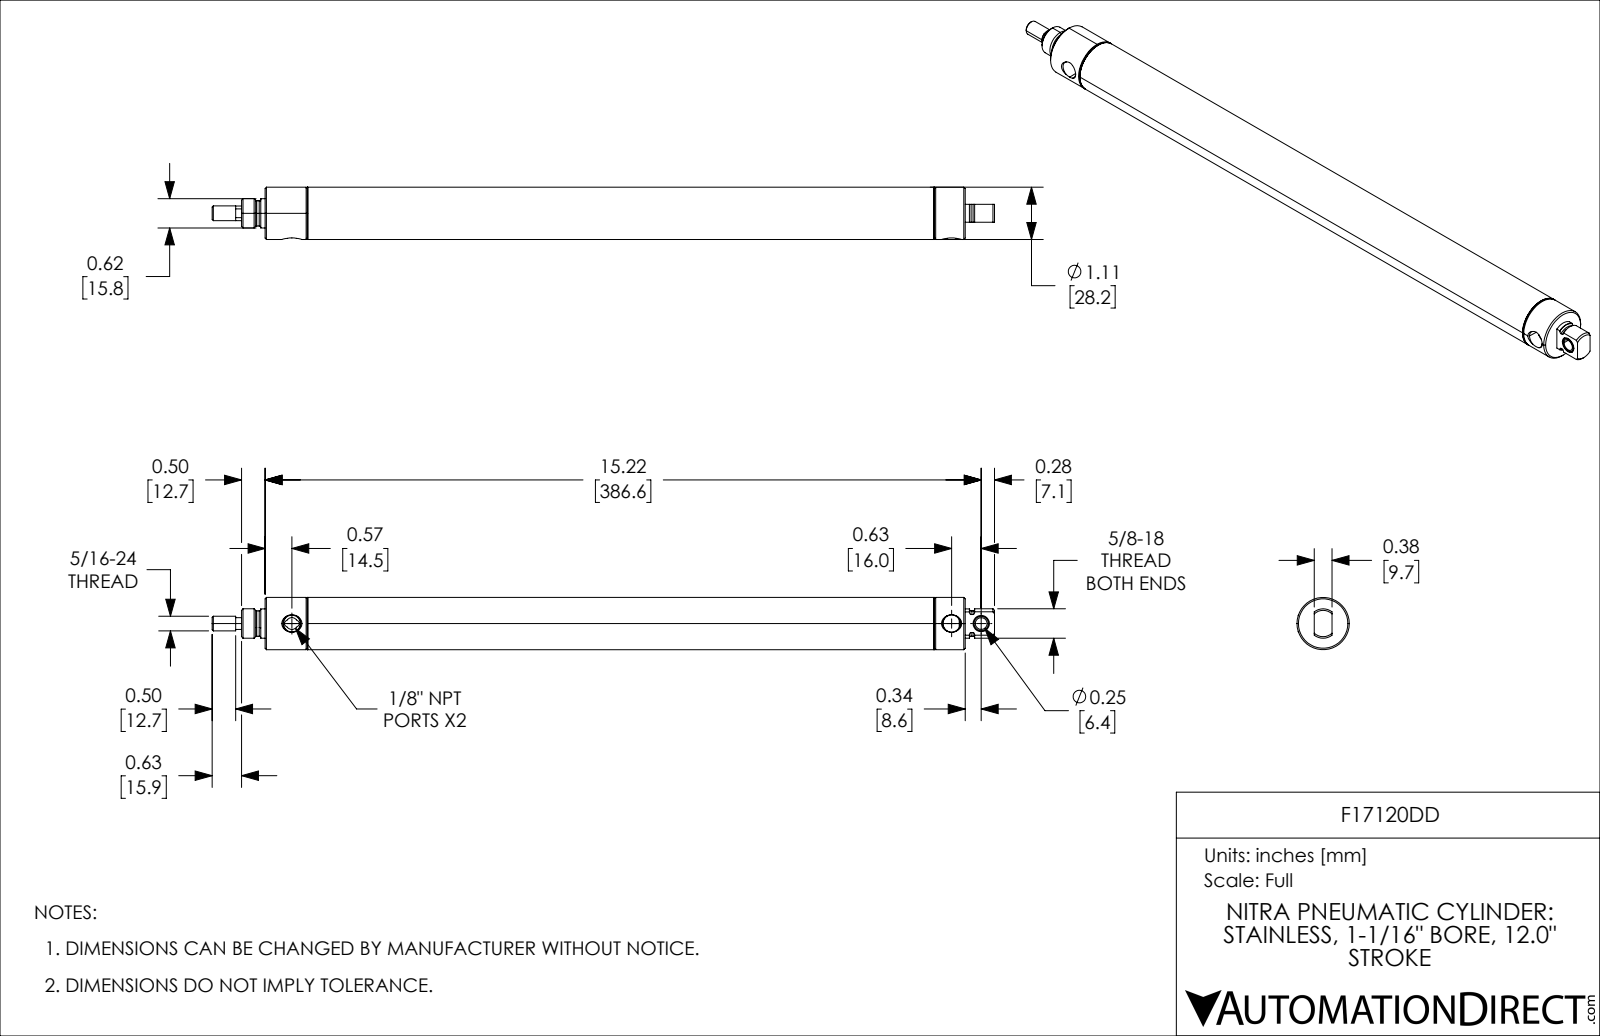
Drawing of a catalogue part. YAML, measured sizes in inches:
part_name: "F17120DD; F17120DD_7; F17120DD_5; F17120DD_9 (+2 more)"
step_written_by: "SolidWorks 2021 (CONFIG_CONTROL_DESIGN)"
units: inches
bodies: {solids: 5, faces: 156, planar: 30, cylindrical: 58, other: 68}
overall_size: [16.625, 1.11, 1.11]
volume: 4.497
surface_area: 128.3
round_holes:
  - {diameter: 0.251, count: 1}
  - {diameter: 0.336, count: 1}
  - {diameter: 0.346, count: 1}
  - {diameter: 0.364, count: 1}
  - {diameter: 0.375, count: 1}
  - {diameter: 0.75, count: 1}
  - {diameter: 1.012, count: 1}
round_bosses_or_shafts:
  - {diameter: 1.11, count: 1}
  - {diameter: 1.072, count: 1}
  - {diameter: 0.625, count: 1}
  - {diameter: 0.622, count: 1}
  - {diameter: 0.539, count: 1}
  - {diameter: 0.313, count: 1}
  - {diameter: 0.312, count: 1}
partial_cylinders:
  - {radius: 0.125, count: 1}
  - {radius: 0.269, count: 1}
face_to_face_distances: [0.875, 12, 12.875, 13.754, 1.754, 0.879, 1.125, 13.125, 14, 14.879]
hole_center_spacings: [0.63]
